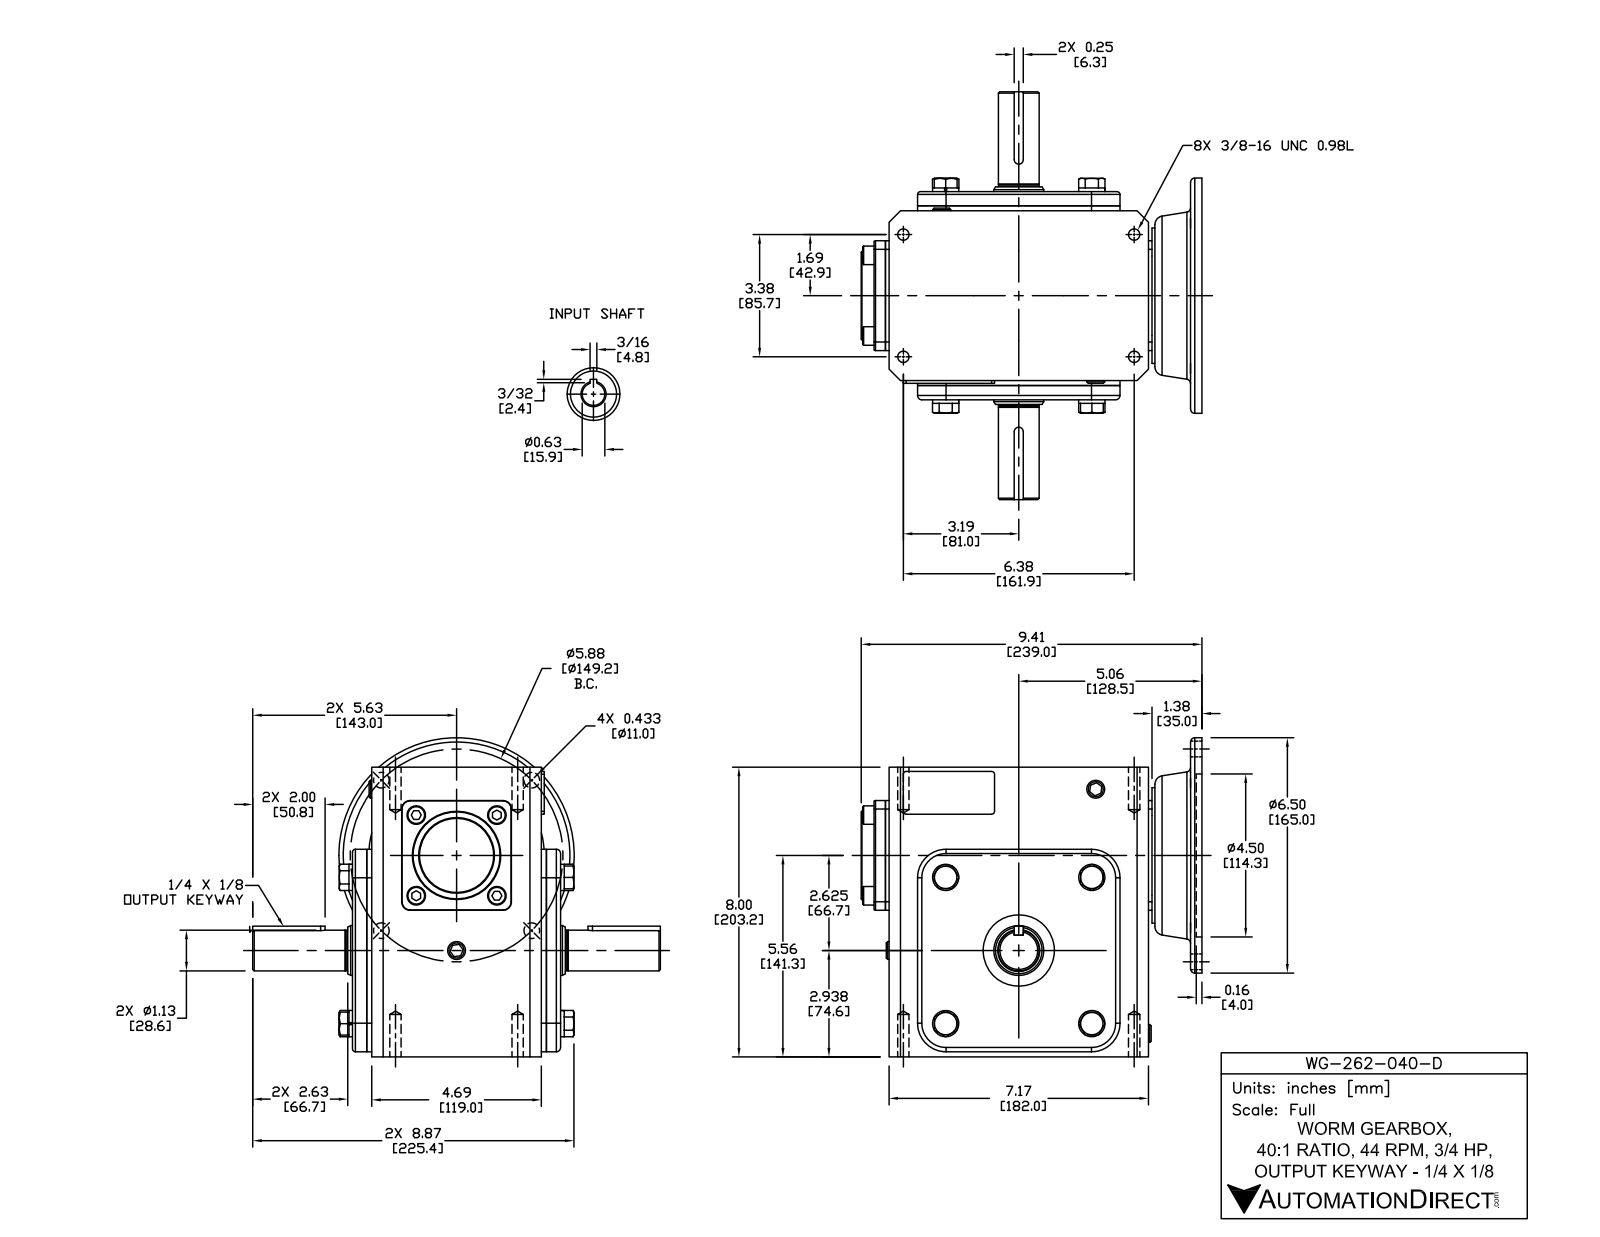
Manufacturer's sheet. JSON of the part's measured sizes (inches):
{"part_name": "WG-262-040-D", "step_written_by": "SolidWorks 2015 (CONFIG_CONTROL_DESIGN)", "units": "inches", "bodies": {"solids": 39, "faces": 562, "planar": 307, "cylindrical": 150, "other": 105}, "overall_size": [11.26, 9.409, 8.811], "volume_in3": 322.1, "surface_area_in2": 632.6, "round_holes": [[0.313, 4], [0.406, 4], [0.591, 1], [0.625, 1], [1.181, 1], [1.378, 1], [1.457, 1], [1.969, 1], [3.819, 1], [4.5, 1]], "round_bosses_or_shafts": [[0.724, 4], [0.512, 4], [6.496, 1], [2.441, 1], [2.047, 1], [1.142, 1], [1.125, 1], [1.113, 1]], "partial_cylinders_radius": [[0.079, 8], [0.118, 8], [0.236, 4], [0.787, 4], [0.02, 2], [0.039, 2], [0.125, 2]], "face_to_face_distances": [4.961, 0.394, 5.354, 5.217, 0.531, 0.138, 4.823, 8, 0.098, 7.264], "hole_center_spacings": [2.937, 4.154, 2.148, 3.375, 5.14, 5.875, 6.375, 7.213]}
